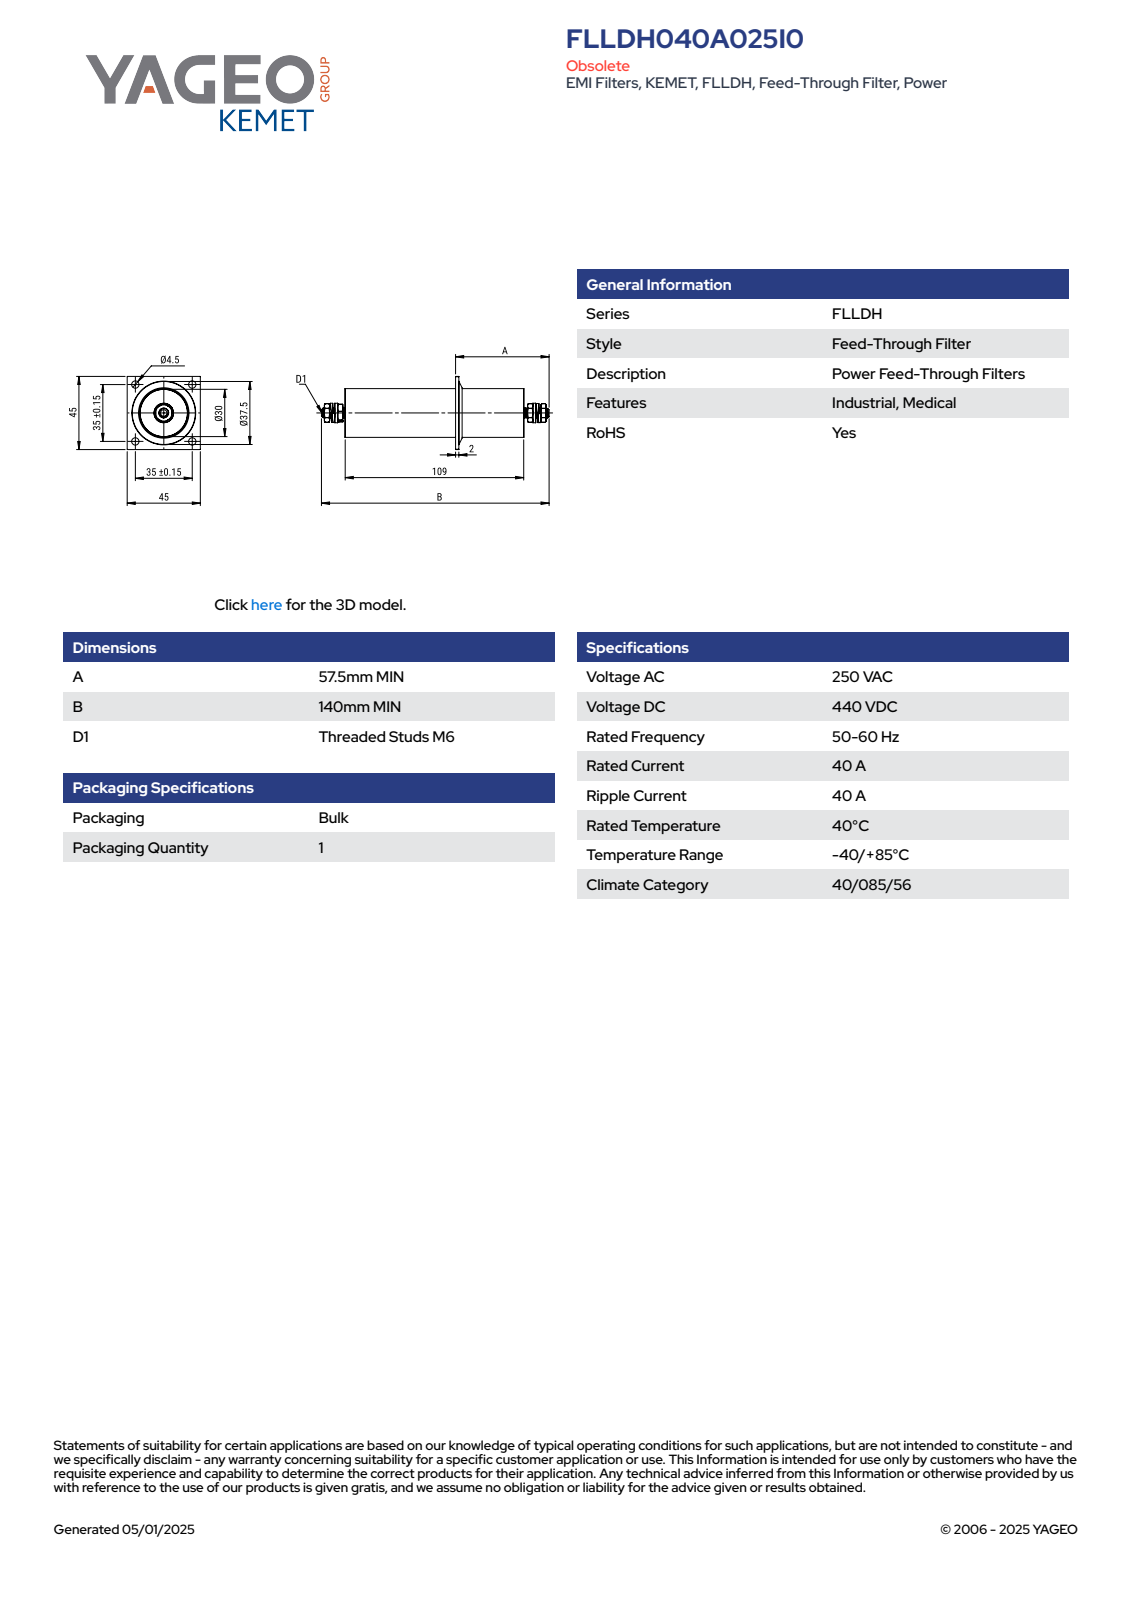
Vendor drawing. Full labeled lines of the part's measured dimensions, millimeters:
Part name (STEP PRODUCT): WASHER M6 Ø12_93475A250; FLLDH025A025I0; DIC0012; GEH0073 (+3 more)
STEP written by: SolidWorks 2021 (AUTOMOTIVE_DESIGN)
Units: millimetres
Bodies: 13 solids, 445 faces (67 planar, 218 cylindrical, 160 other)
Overall size (bounding box): 140 × 45 × 45
Volume: 13 693 mm³ · Surface area: 30 833 mm²
Round holes (diameter × count): ⌀4.5 ×4, ⌀6.1 ×1, ⌀6.4 ×1, ⌀29 ×1
Round bosses / shafts (diameter × count): ⌀30 ×1, ⌀29.1 ×1, ⌀12 ×1, ⌀6 ×1
Partial cylindrical surfaces — rounded edges, fillets, slot ends (radius × count): R0.2 ×16, R0.5 ×4
Main face-to-face distances: 2, 68, 40, 108, 70, 42, 110, 38, 66, 106
Hole centre spacings: 24.75, 35, 49.5
